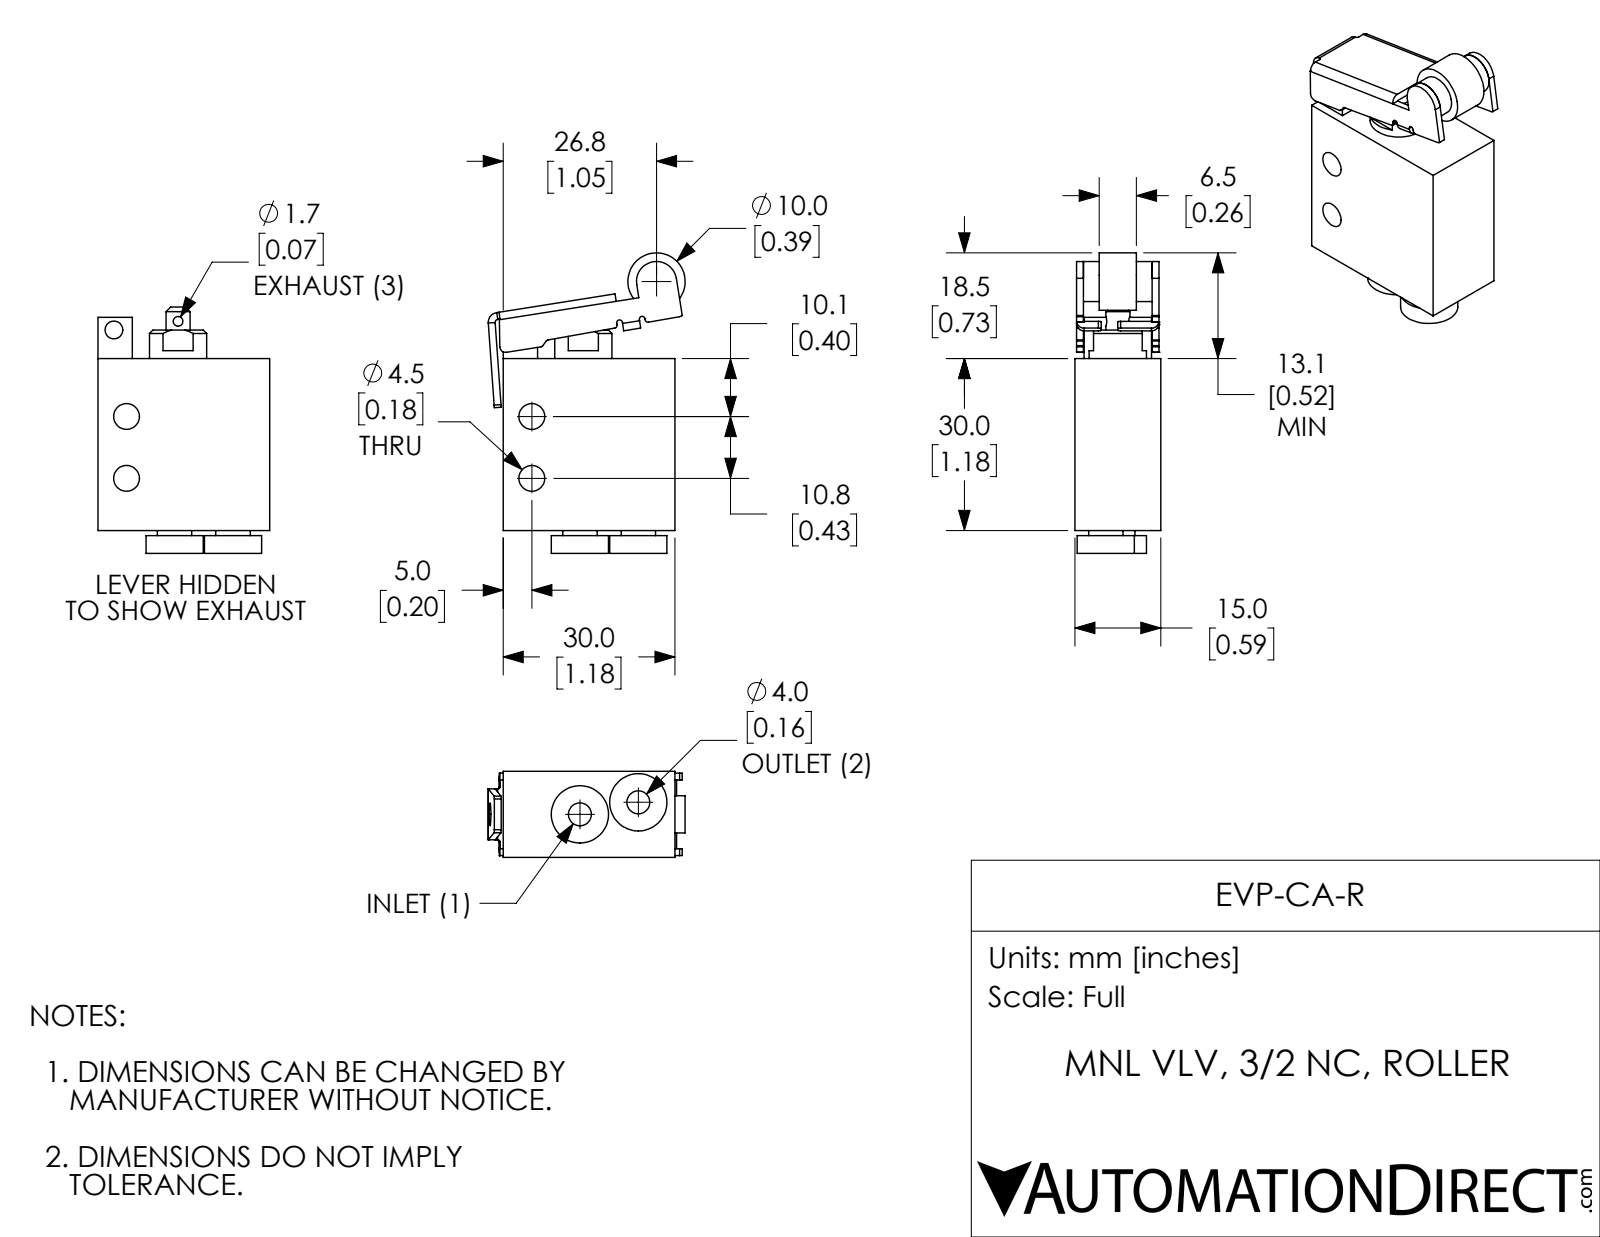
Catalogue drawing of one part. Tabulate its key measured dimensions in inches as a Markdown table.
| quantity | value |
| --- | --- |
| part name | EVP-CA-R |
| STEP written by | SolidWorks 2017 (AUTOMOTIVE_DESIGN) |
| units | inches |
| bodies | 3 solids, 148 faces (74 planar, 70 cylindrical, 4 other) |
| overall size | 2.065 × 1.353 × 0.591 |
| volume | 0.996 in³ |
| surface area | 11.91 in² |
| round holes (diameter × count) | 0.157 × 3, 0.177 × 2, 0.067 × 1, 0.122 × 1 |
| round bosses / shafts (diameter × count) | 0.394 × 4, 0.236 × 2, 0.276 × 1, 0.197 × 1, 0.165 × 1 |
| partial cylindrical surfaces (radius × count) | 0.02 × 13, 0.051 × 4, 0.004 × 2, 0.016 × 2, 0.039 × 2, 0.067 × 1 |
| main face-to-face distances | 0.591, 1.181, 0.047, 0.059, 0.531, 0.579, 0.52, 0.048, 0.472, 0.567 |
| hole center spacings | 0.41, 0.425, 0.445, 0.601, 0.743, 1.023, 1.135 |
